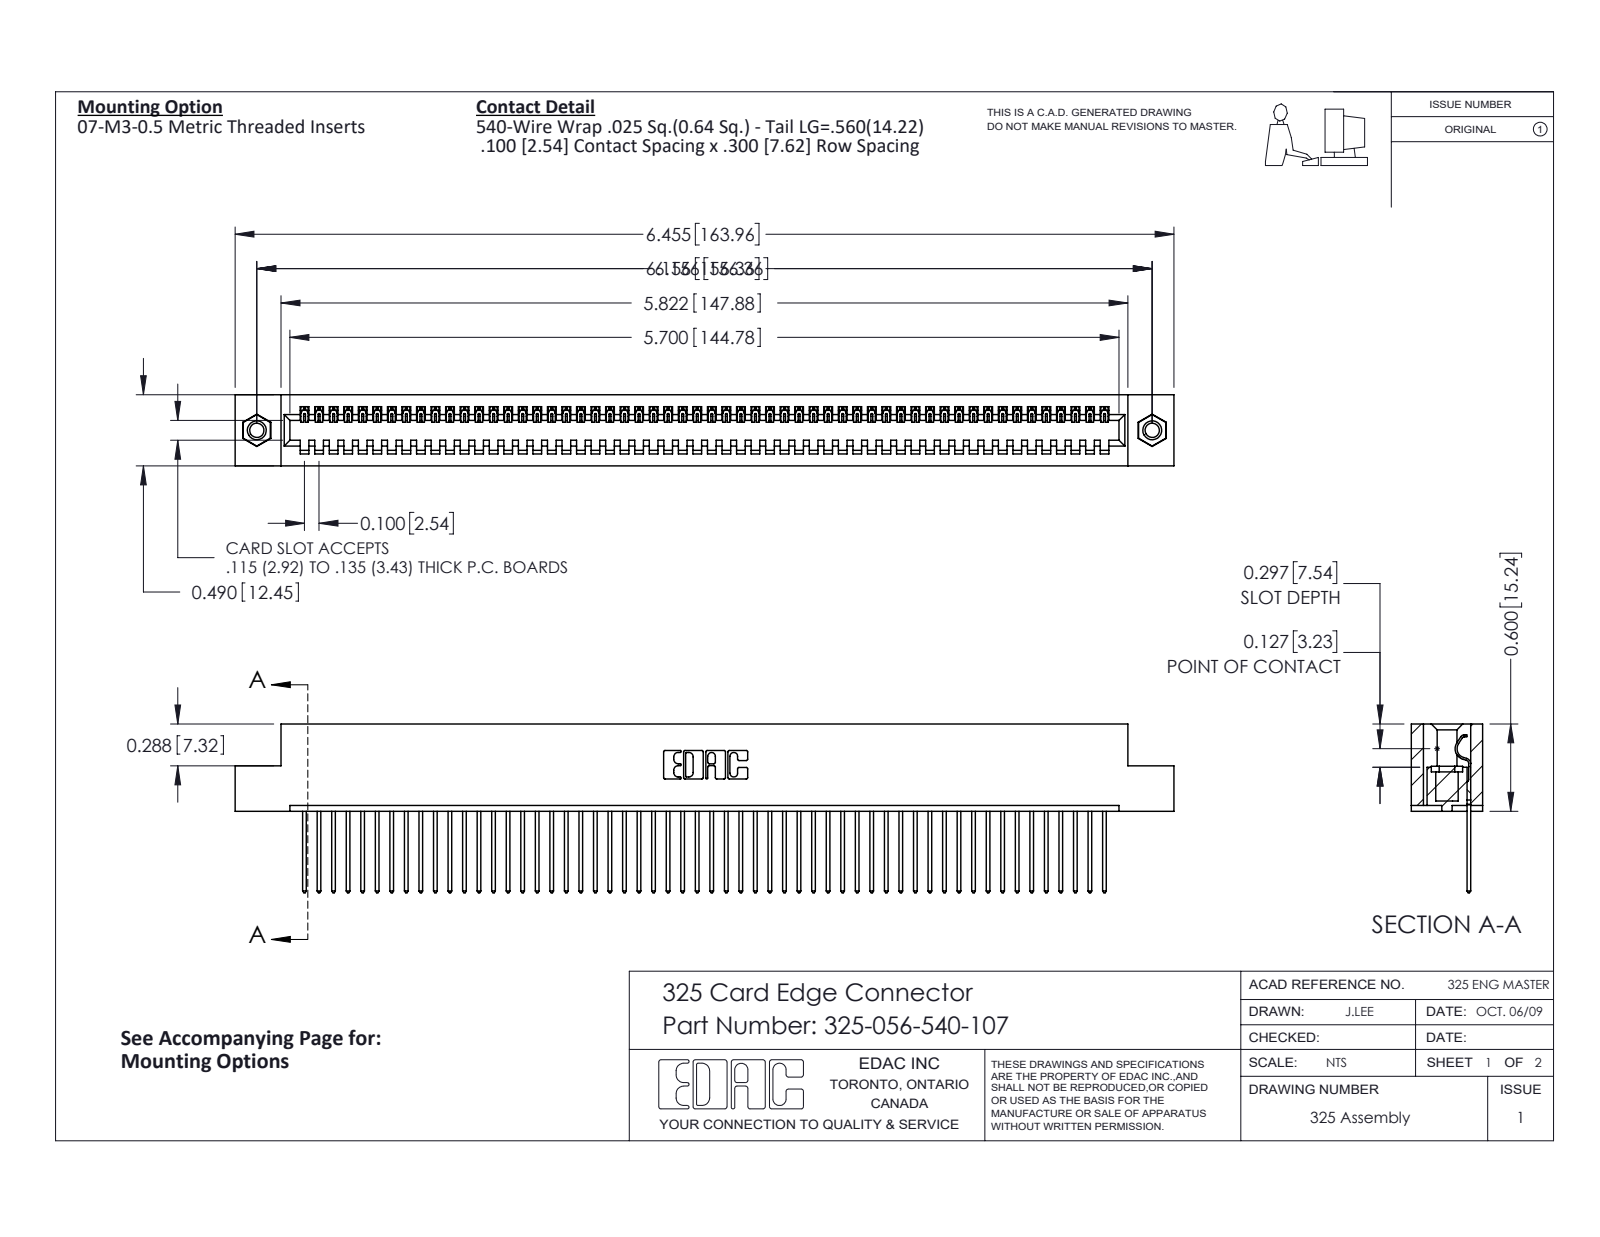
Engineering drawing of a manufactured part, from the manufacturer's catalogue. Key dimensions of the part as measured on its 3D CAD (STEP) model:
Part name (STEP PRODUCT): 325 Part_TI; 345-250-001_345-250-005-103; 325-292-001_325-293-140; 325-056-540-107
STEP written by: SolidWorks 2016 (CONFIG_CONTROL_DESIGN)
Units: inches
Bodies: 59 solids, 3422 faces (2454 planar, 952 cylindrical, 16 other)
Overall size (bounding box): 6.455 × 1.16 × 0.49
Volume: 1.281 in³ · Surface area: 36.82 in²
Round holes (diameter × count): ⌀0.098 ×2, ⌀0.125 ×2, ⌀0.16 ×2
Round bosses / shafts (diameter × count): ⌀0.155 ×2
Partial cylindrical surfaces — rounded edges, fillets, slot ends (radius × count): R0.006 ×112, R0.01 ×112, R0.01 ×22, R0.007 ×6, R0.031 ×6, R0.026 ×3, R0.014 ×1, R0.022 ×1
Main face-to-face distances: 0.083, 0.407, 0.49, 0.107, 0.383, 0.025, 0.3, 0.325, 0.56, 0.263
Hole centre spacings: 6.156
